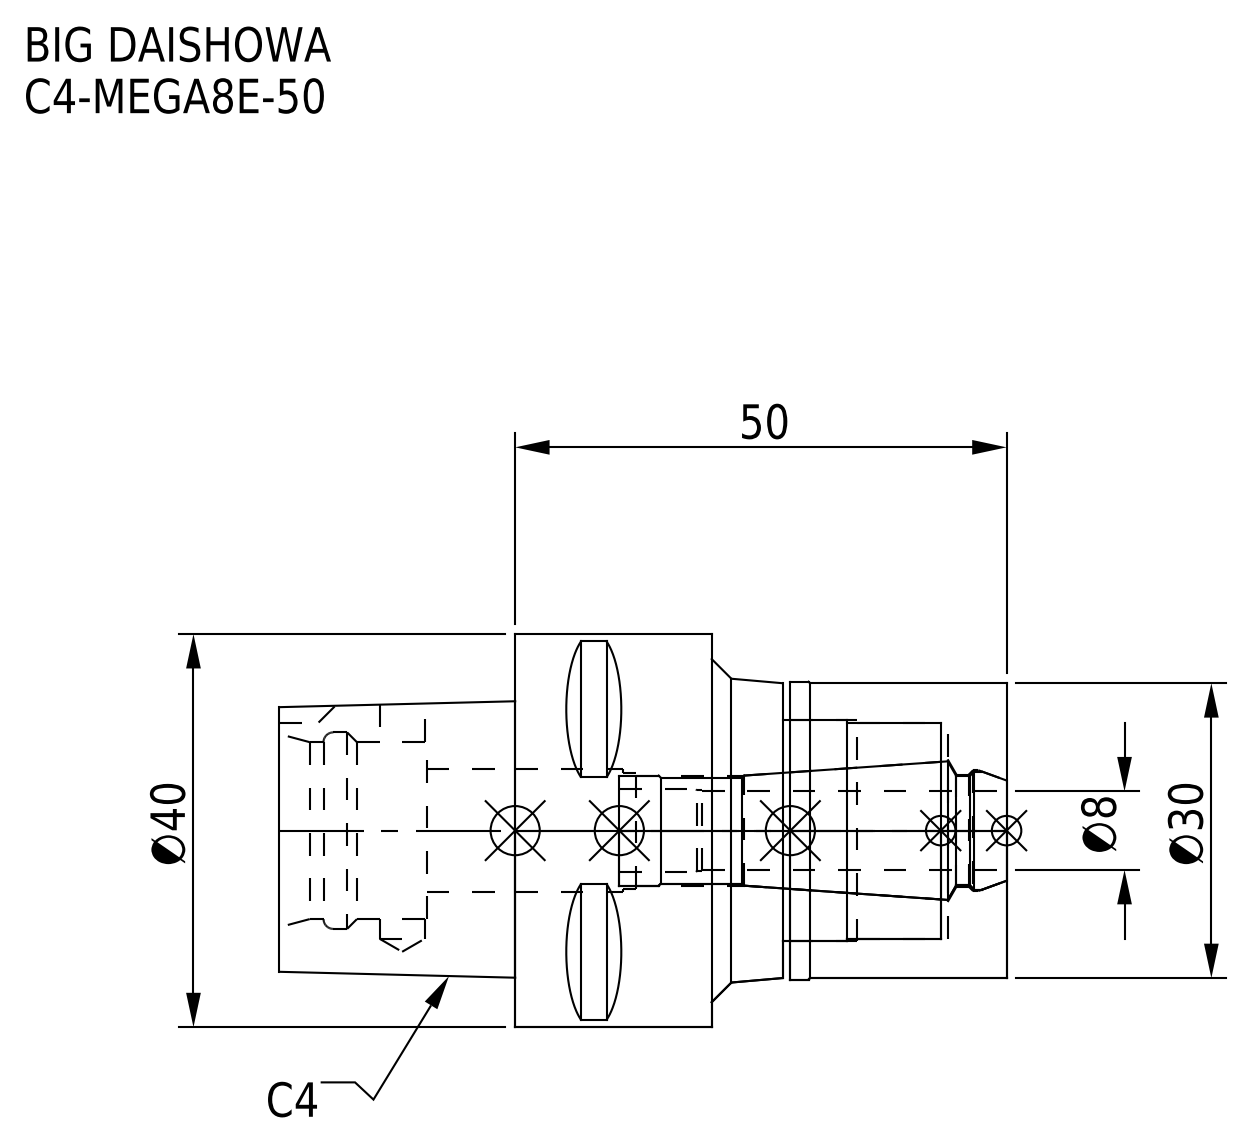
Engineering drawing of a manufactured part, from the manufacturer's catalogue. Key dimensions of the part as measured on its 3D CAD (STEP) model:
Part name (STEP PRODUCT): C4-MEGA8E-50-080_ASM.stp; C4-MEGA8E-50_1.stp; C4-MEGA8E-50-080-FreeParts; MEN8_1.stp (+3 more)
STEP written by: SolidWorks 2019 (CONFIG_CONTROL_DESIGN)
Units: millimetres
Bodies: 2 solids, 94 faces (35 planar, 35 cylindrical, 24 other)
Overall size (bounding box): 74 × 40 × 40
Volume: 48 838 mm³ · Surface area: 16 191 mm²
Round holes (diameter × count): ⌀4.6 ×1, ⌀11.2 ×1, ⌀11.4 ×1, ⌀11.8 ×1, ⌀12.3 ×1, ⌀12.5 ×1, ⌀18 ×1, ⌀20 ×1, ⌀22 ×1, ⌀22.5 ×1
Round bosses / shafts (diameter × count): ⌀40 ×1, ⌀30.3 ×1, ⌀30 ×1
Partial cylindrical surfaces — rounded edges, fillets, slot ends (radius × count): R3 ×1
Main face-to-face distances: 50, 24, 44, 22, 28, 22.8, 20, 0.8, 27.2, 30
